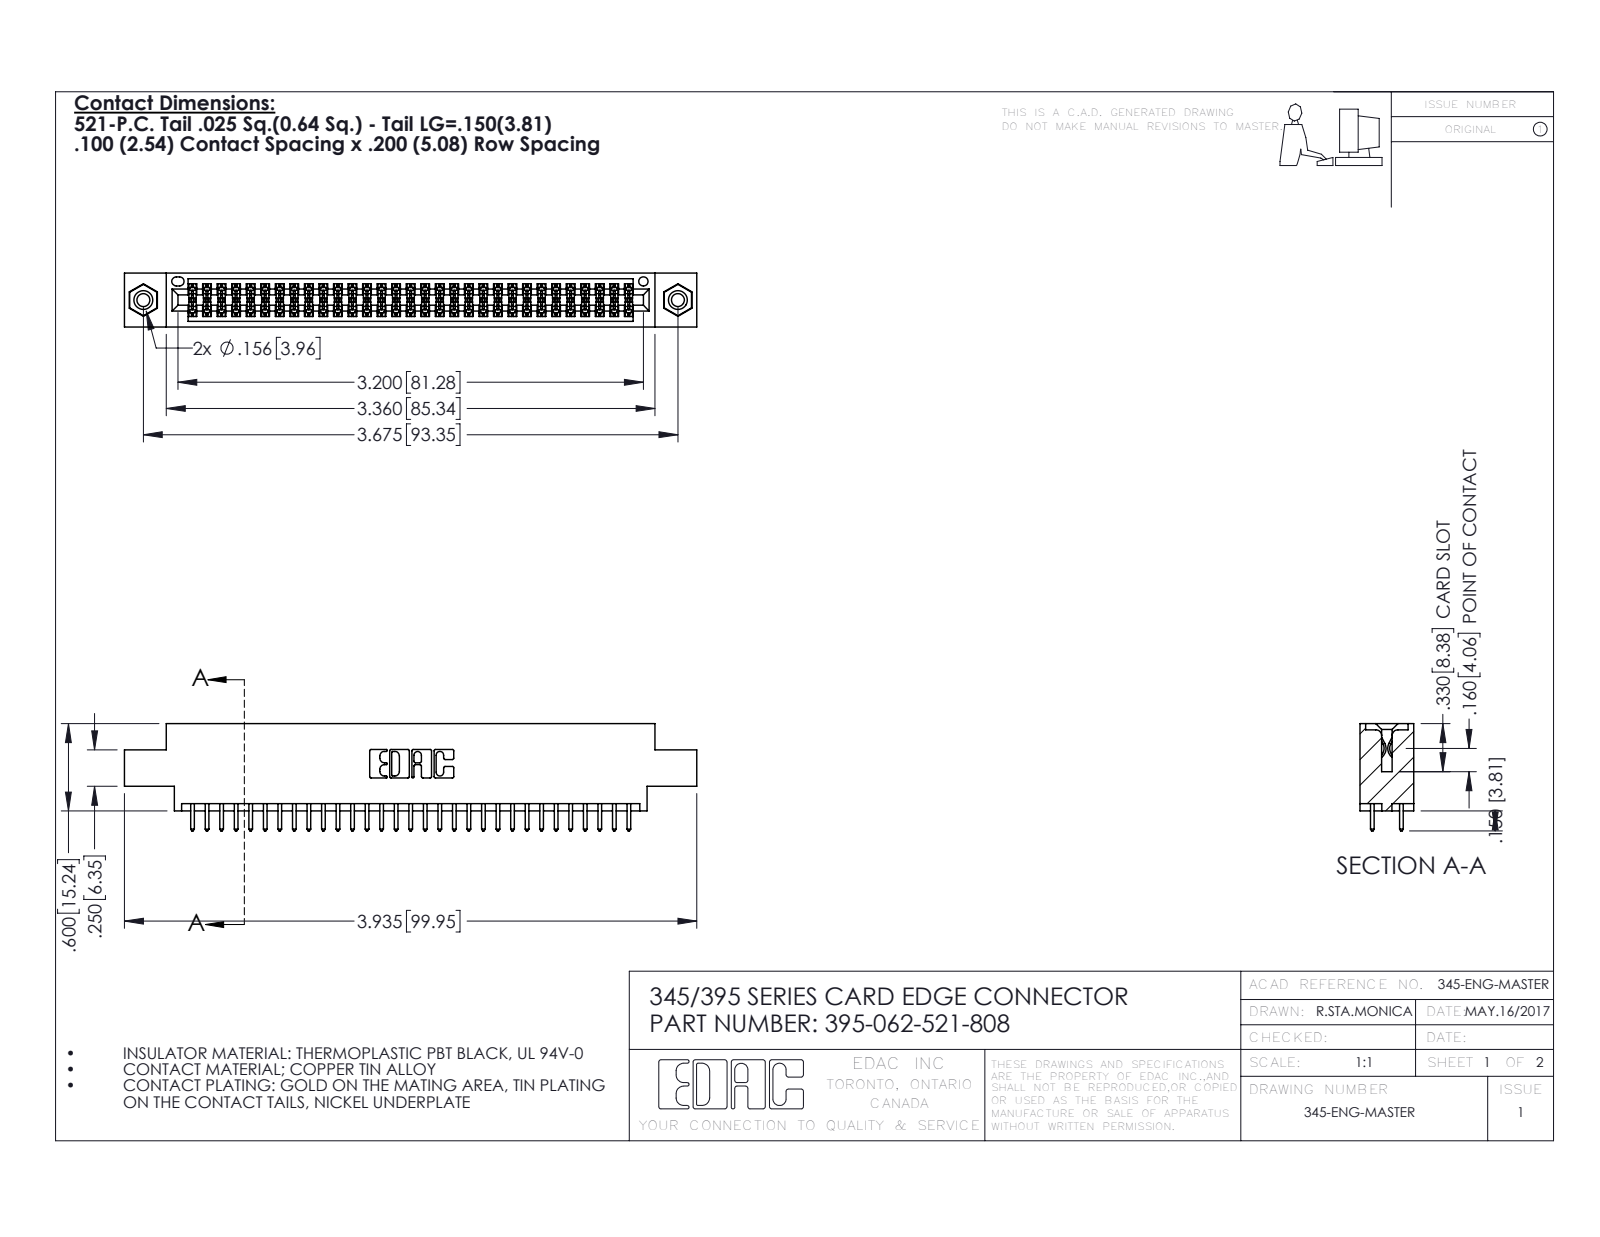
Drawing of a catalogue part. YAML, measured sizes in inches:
part_name: "345-292-001_345-293-121; 345-250-001_345-250-003-102; 395-062-521-808; 345 Part_0.170 Offset - 0.156 Dia-TI"
step_written_by: "SolidWorks 2016 (CONFIG_CONTROL_DESIGN)"
units: inches
bodies: {solids: 65, faces: 3290, planar: 2162, cylindrical: 1112, other: 16}
overall_size: [3.935, 0.737, 0.37]
volume: 0.577
surface_area: 21.34
round_holes:
  - {diameter: 0.089, count: 2}
  - {diameter: 0.125, count: 2}
  - {diameter: 0.156, count: 2}
  - {diameter: 0.064, count: 1}
round_bosses_or_shafts:
  - {diameter: 0.155, count: 2}
partial_cylinders:
  - {radius: 0.006, count: 93}
  - {radius: 0.01, count: 62}
  - {radius: 0.01, count: 22}
  - {radius: 0.007, count: 6}
  - {radius: 0.031, count: 6}
  - {radius: 0.026, count: 3}
  - {radius: 0.014, count: 2}
  - {radius: 0.019, count: 2}
face_to_face_distances: [0.072, 0.298, 0.2, 0.37, 0.098, 0.272, 0.025, 0.225, 0.175, 0.149]
hole_center_spacings: [0.27, 3.44, 3.675]
